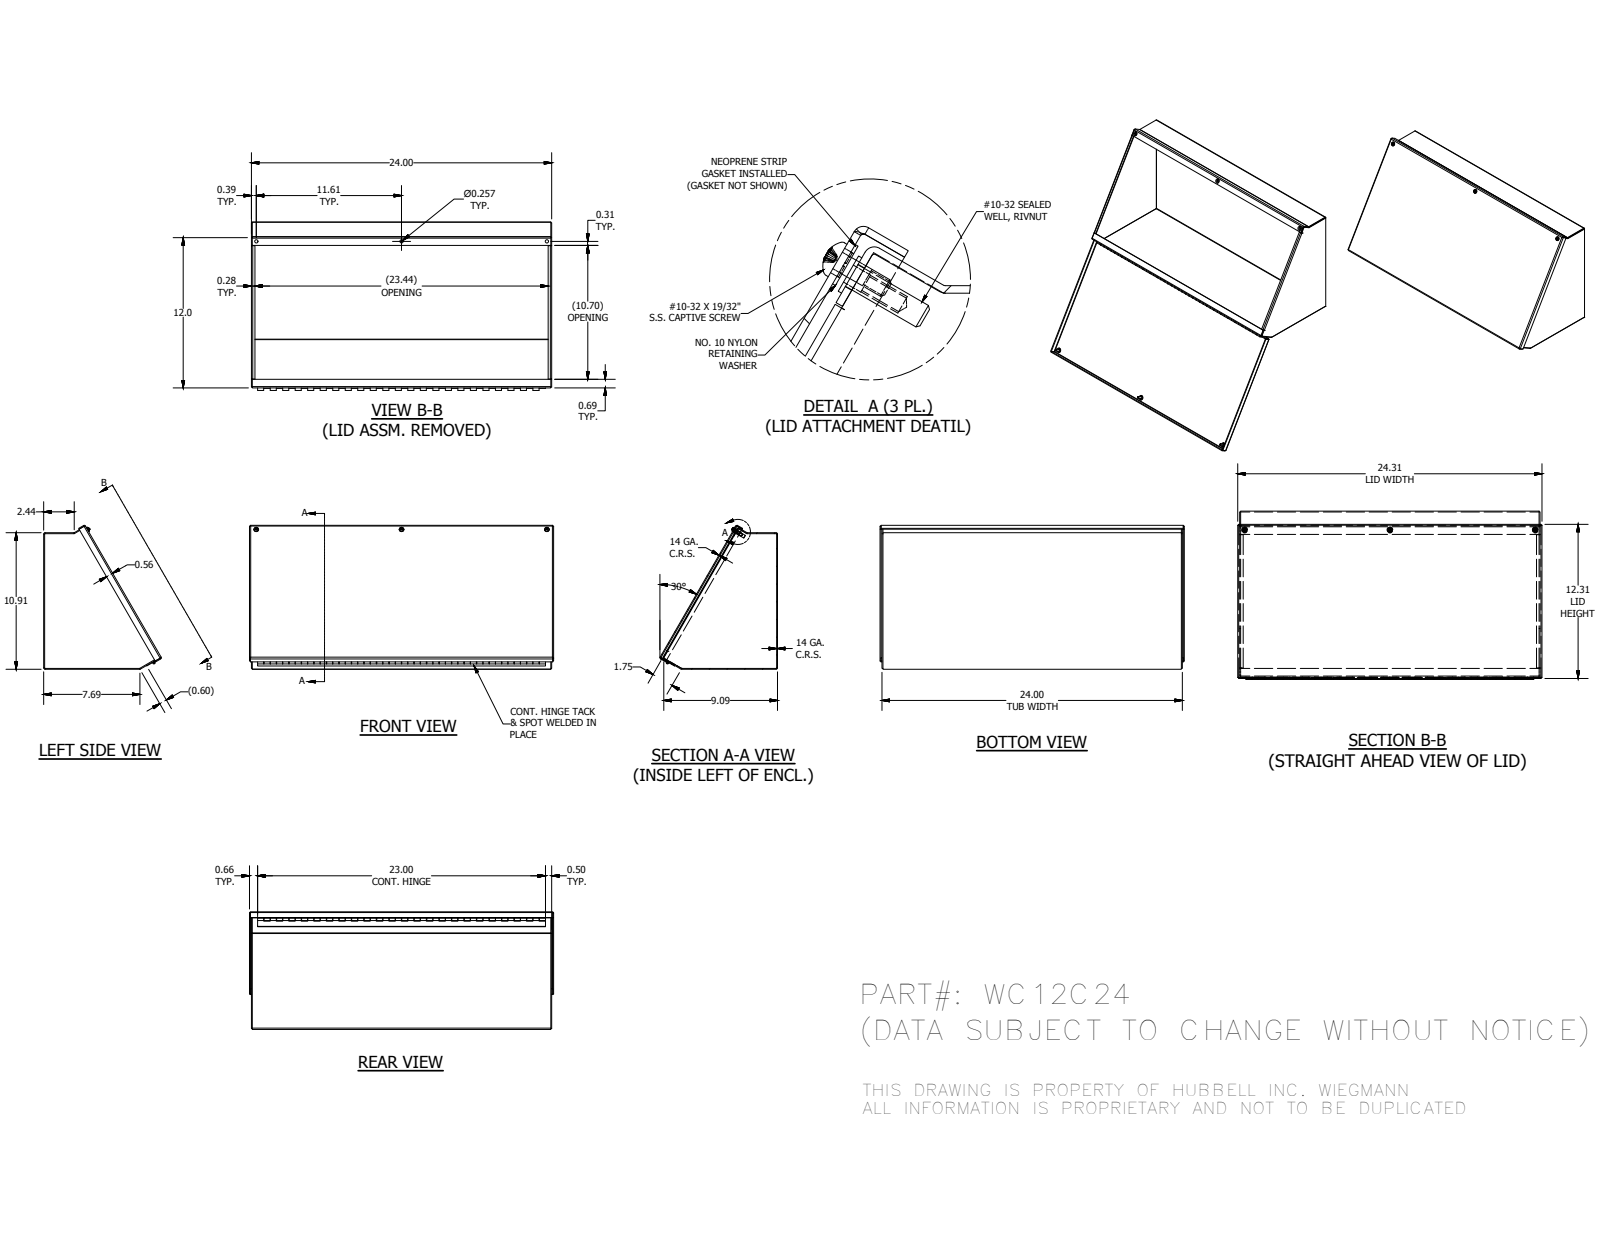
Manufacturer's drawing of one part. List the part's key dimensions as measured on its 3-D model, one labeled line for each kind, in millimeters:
Part name (STEP PRODUCT): WC12C24BTB; WC12C24LID; WC12CLS; WC12CRS (+8 more)
STEP written by: Autodesk Inventor 2014 (AUTOMOTIVE_DESIGN)
Units: millimetres
Bodies: 16 solids, 597 faces (364 planar, 159 cylindrical, 74 other)
Overall size (bounding box): 617.54 × 292.07 × 238.63
Volume: 1 316 000 mm³ · Surface area: 1 437 000 mm²
Round holes (diameter × count): ⌀3.96 ×3, ⌀4.98 ×3, ⌀6.53 ×3, ⌀7.06 ×3, ⌀7.14 ×3, ⌀2.96 ×1
Round bosses / shafts (diameter × count): ⌀11.51 ×3, ⌀10.31 ×3, ⌀9.47 ×3, ⌀6.3 ×3, ⌀4.83 ×3, ⌀5.08 ×1, ⌀2.54 ×1
Partial cylindrical surfaces — rounded edges, fillets, slot ends (radius × count): R0.79 ×12, R2.67 ×12, R2.27 ×3
Main face-to-face distances: 1.88, 607.72, 275.14, 605.84, 609.6, 273.26, 277.02, 2.94, 304.8, 1.06
Hole centre spacings: 294.97, 589.94, 1.51
